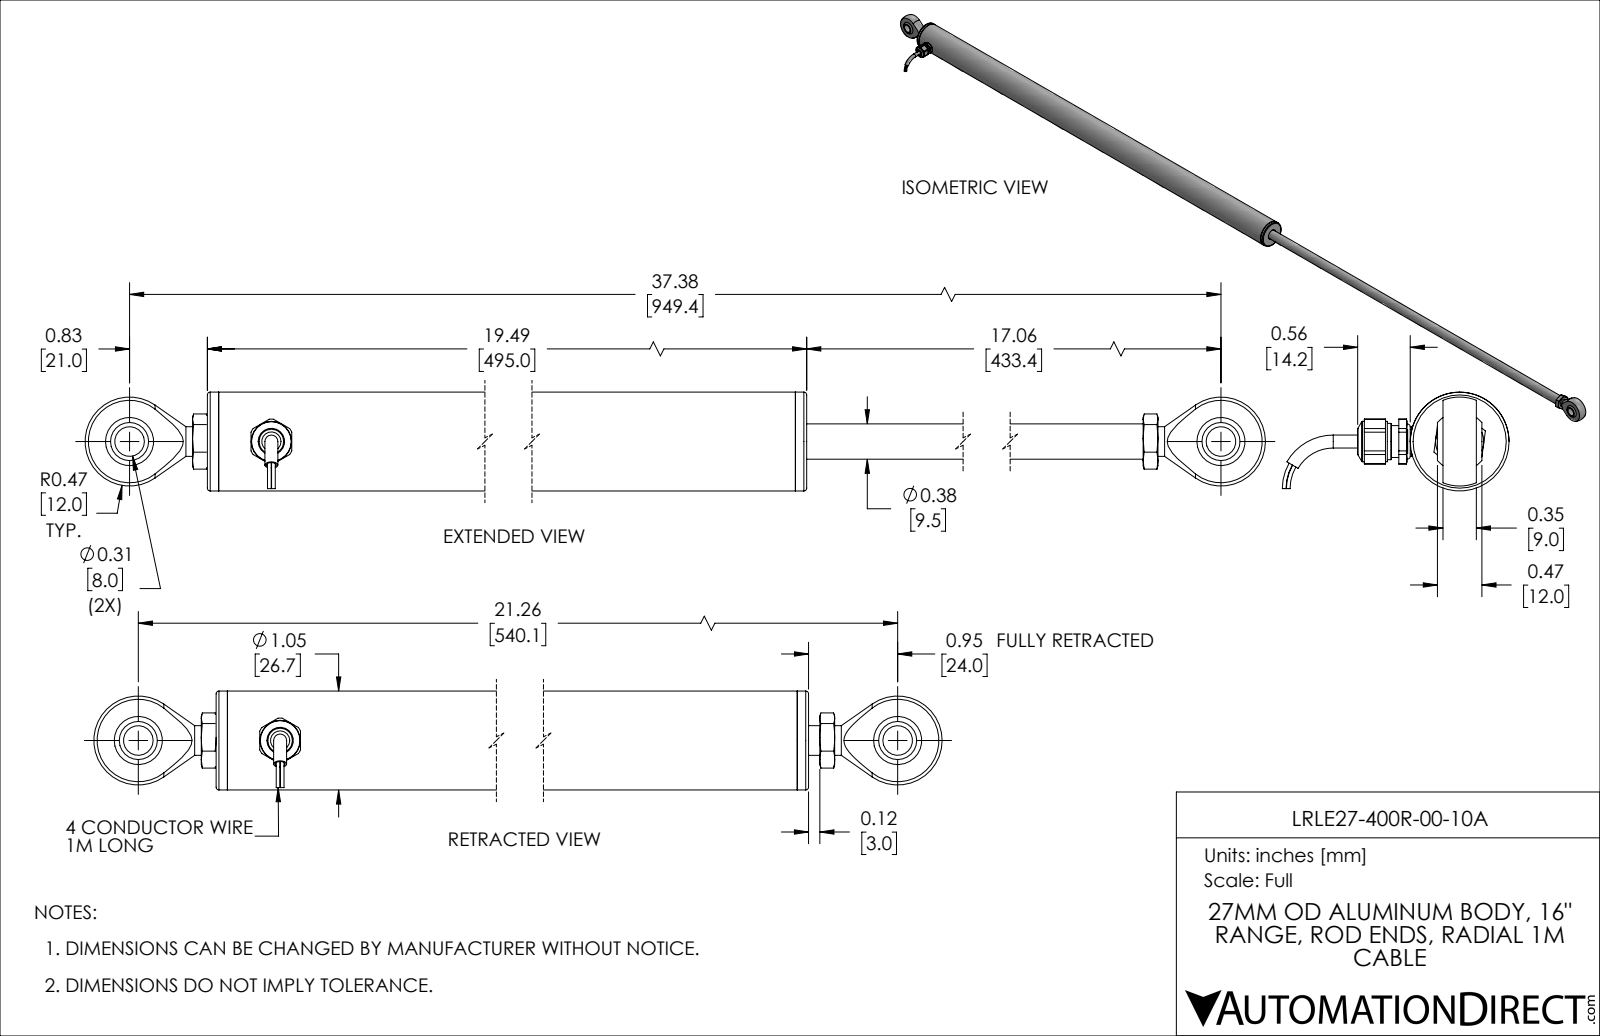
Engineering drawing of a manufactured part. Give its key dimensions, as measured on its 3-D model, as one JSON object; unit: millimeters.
{"part_name": "LRLE27-400R-00-10A", "step_written_by": "SolidWorks 2019 (AUTOMOTIVE_DESIGN)", "units": "millimeters", "bodies": {"solids": 28, "faces": 298, "planar": 114, "cylindrical": 92, "other": 92}, "overall_size": [561, 61.2, 26.7], "volume_mm3": 159000, "surface_area_mm2": 127900, "round_holes": [[6.8, 2], [8, 2], [2.7, 1], [3.5, 1], [4, 1], [4.7, 1], [5.1, 1], [5.2, 1], [6.4, 1], [7, 1], [8, 1], [9.1, 1]], "round_bosses_or_shafts": [[1, 4], [8, 2], [26.7, 1], [21.6, 1], [21.5, 1], [17.4, 1], [15.9, 1], [12.7, 1]], "partial_cylinders_radius": [[0.3, 2], [1.7, 2], [6.4, 2], [5, 1], [5.7, 1], [6, 1], [8.7, 1], [10.3, 1]], "face_to_face_distances": [9, 495, 18.7, 476.3, 3, 492, 12.7, 41.9, 23.2, 453.1], "hole_center_spacings": [38.3, 498.8, 537.1]}
